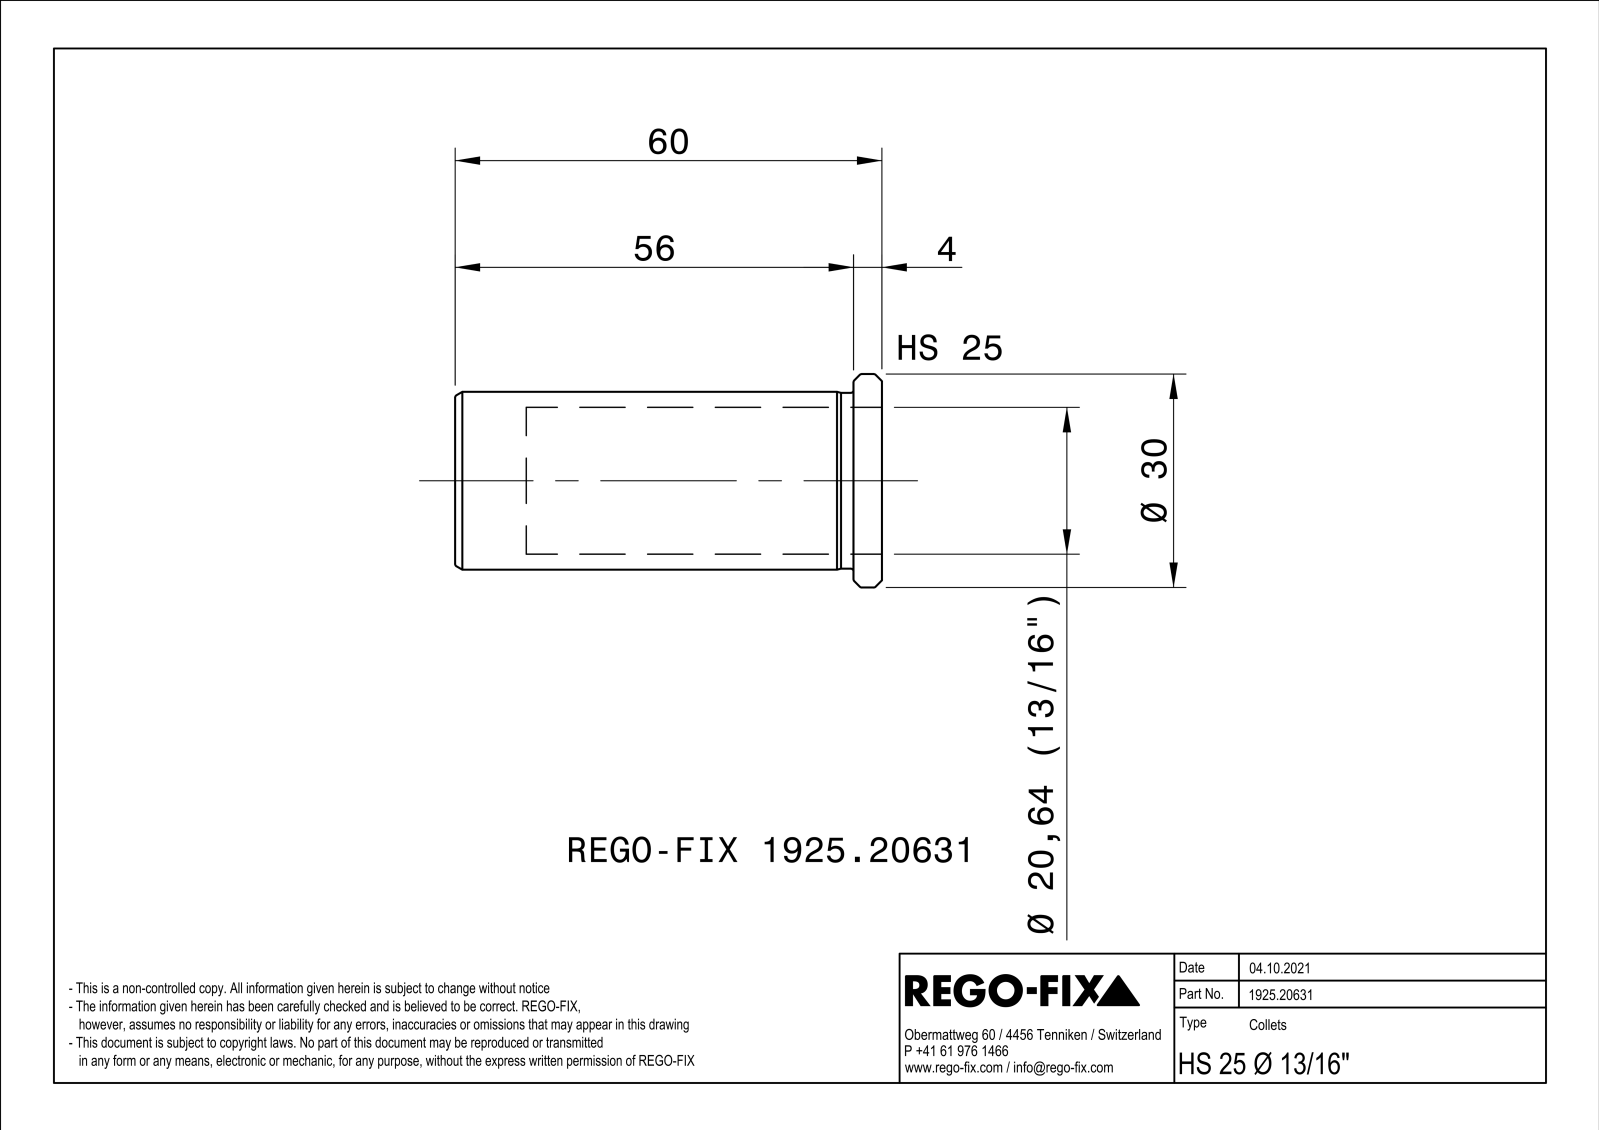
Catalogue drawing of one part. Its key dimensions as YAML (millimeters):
part_name: "NOCUT"
step_written_by: "SIEMENS PLM Software Solid Edge ST10 (AUTOMOTIVE_DESIGN)"
units: millimeters
bodies: {solids: 1, faces: 70, planar: 22, cylindrical: 11, other: 37}
overall_size: [60, 29.98, 29.98]
volume: 9630
surface_area: 9641
round_holes:
  - {diameter: 20.64, count: 1}
  - {diameter: 21, count: 1}
round_bosses_or_shafts:
  - {diameter: 30, count: 1}
  - {diameter: 25, count: 1}
  - {diameter: 24.7, count: 1}
face_to_face_distances: [1, 4, 60, 56]
